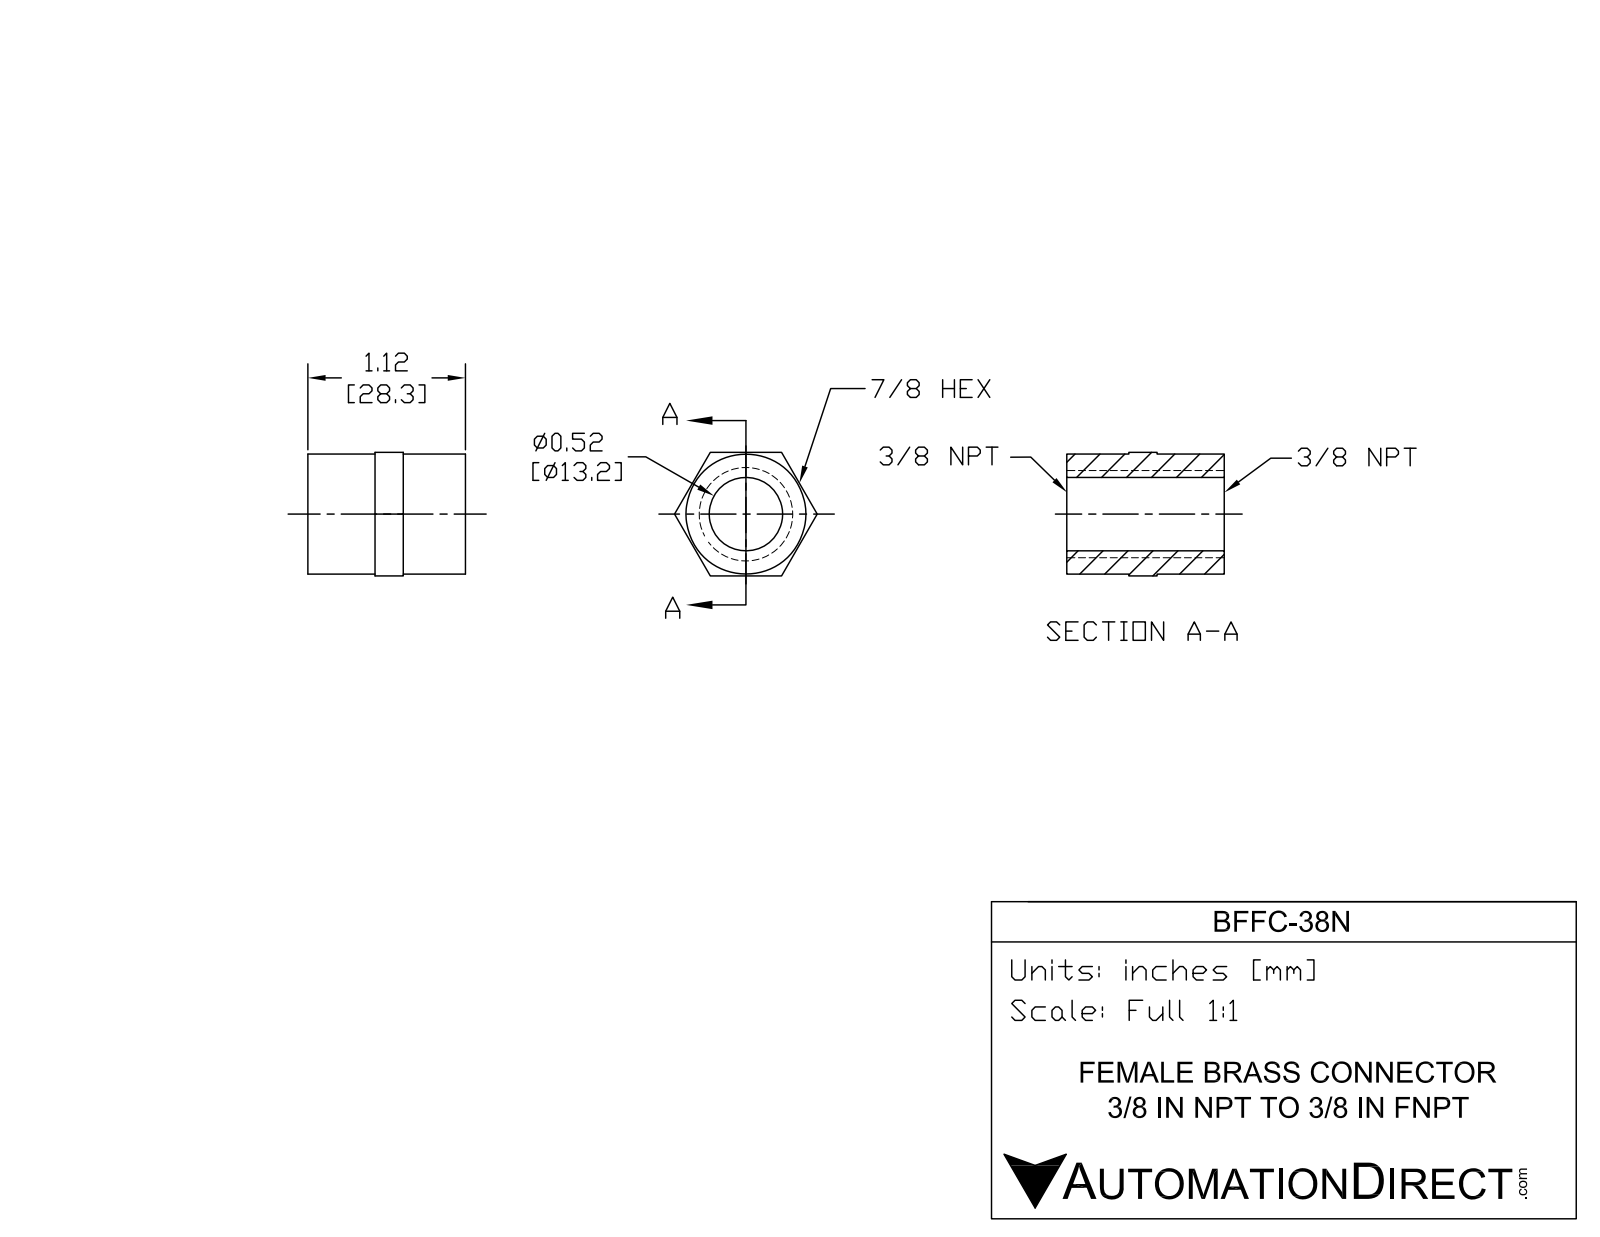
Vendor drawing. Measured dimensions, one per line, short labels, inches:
name: BFFC-38N
written by: SolidWorks 2015 (CONFIG_CONTROL_DESIGN)
unit: in
bodies: 1 solid, 16 faces (10 planar, 6 cylindrical, 0 other)
size: 1.116 × 1.01 × 0.875
volume: 0.373 in³; area: 5.858 in²
holes: 1× ⌀0.565
bosses: 1× ⌀0.85
face distances: 1.116, 0.875, 0.476, 0.676, 0.2, 0.64, 0.44
